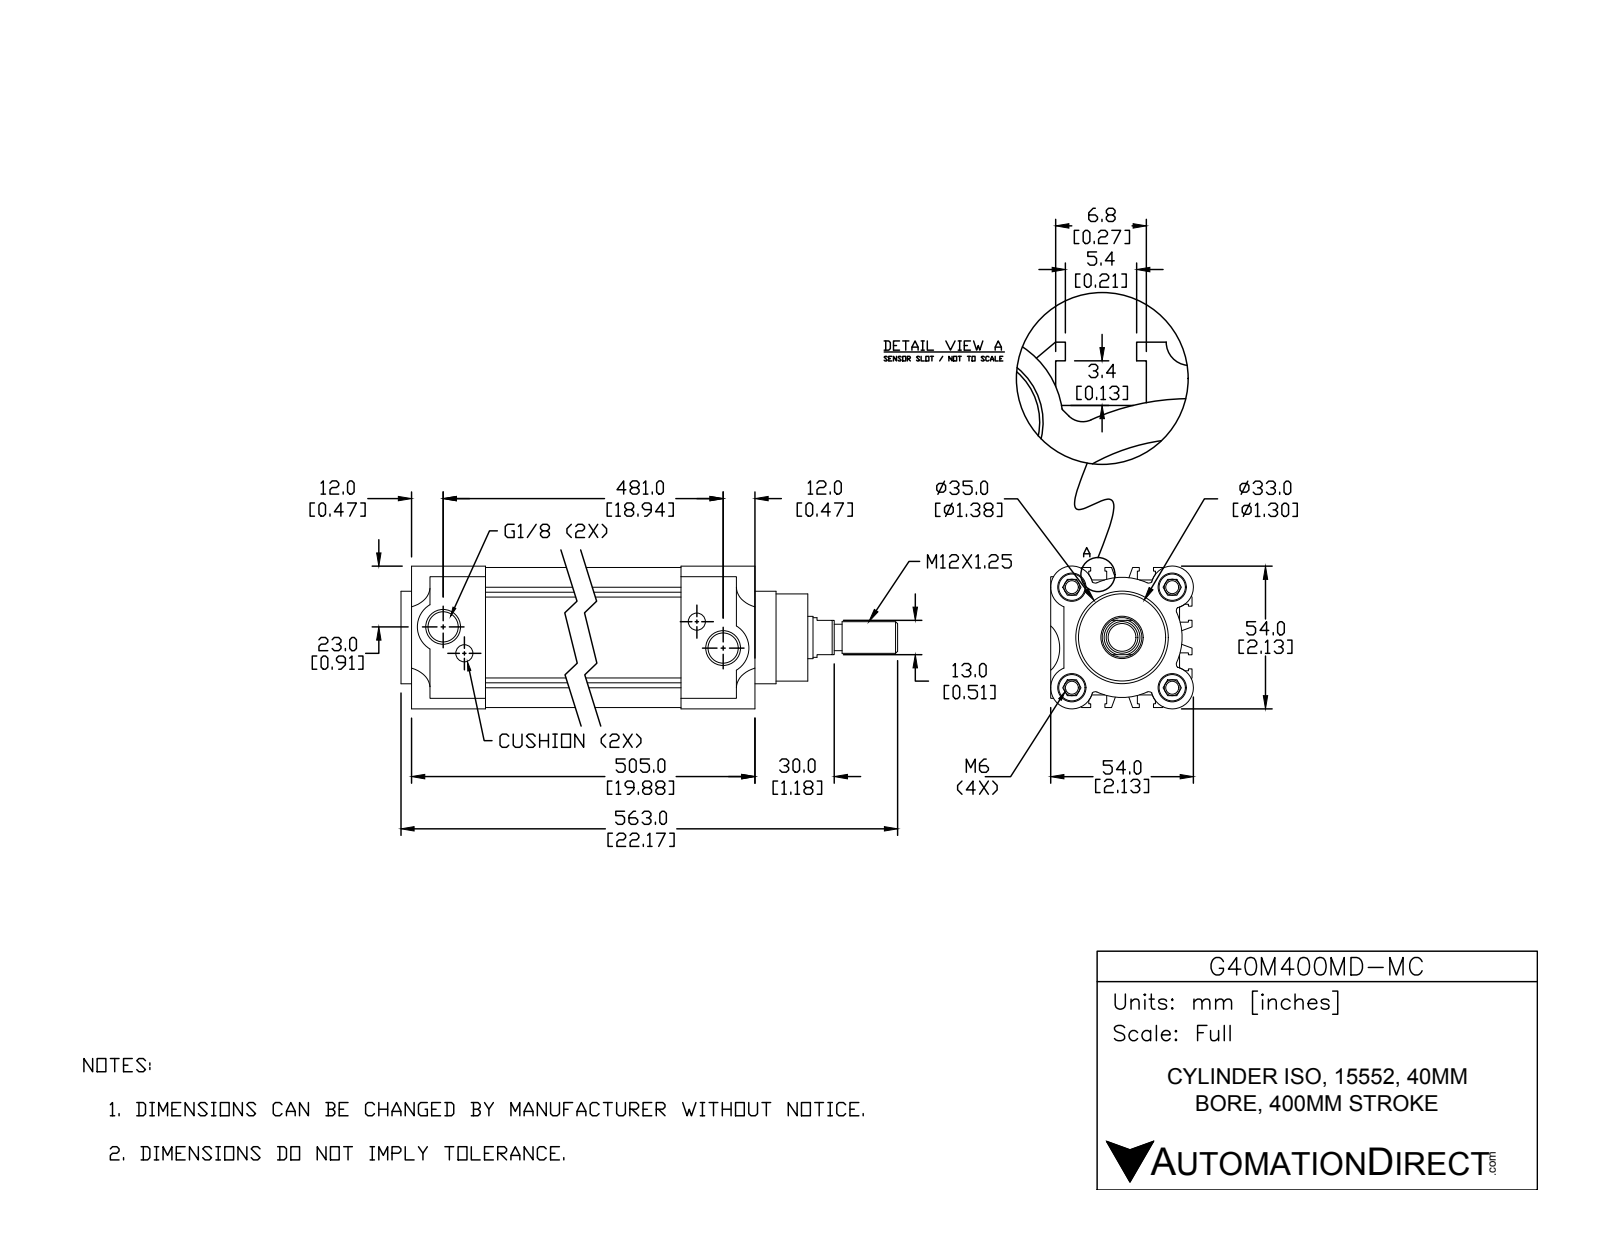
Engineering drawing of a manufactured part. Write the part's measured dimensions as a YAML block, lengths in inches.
part_name: "G40M400MD-MC; 40121400-R; 40121-HR; 40-400-83-B (+1 more)"
step_written_by: "SolidWorks 2015 (CONFIG_CONTROL_DESIGN)"
units: inches
bodies: {solids: 4, faces: 419, planar: 236, cylindrical: 138, other: 45}
overall_size: [22.165, 2.126, 2.126]
volume: 51.42
surface_area: 415.6
round_holes:
  - {diameter: 0.194, count: 4}
  - {diameter: 0.421, count: 4}
  - {diameter: 0.256, count: 2}
  - {diameter: 0.451, count: 2}
  - {diameter: 0.63, count: 1}
round_bosses_or_shafts:
  - {diameter: 0.394, count: 5}
  - {diameter: 1.575, count: 1}
  - {diameter: 1.378, count: 1}
  - {diameter: 1.299, count: 1}
  - {diameter: 0.591, count: 1}
  - {diameter: 0.472, count: 1}
partial_cylinders:
  - {radius: 0.059, count: 12}
  - {radius: 0.004, count: 6}
  - {radius: 0.295, count: 4}
  - {radius: 0.315, count: 4}
  - {radius: 0.384, count: 2}
  - {radius: 0.886, count: 1}
  - {radius: 0.896, count: 1}
face_to_face_distances: [1.9, 0.187, 2.087, 0.724, 0.954, 1.372, 0.547, 1.539, 0.815, 1.272]
hole_center_spacings: [1.058, 1.496, 2.116, 0.504, 0.557, 18.235, 18.543, 18.622]
